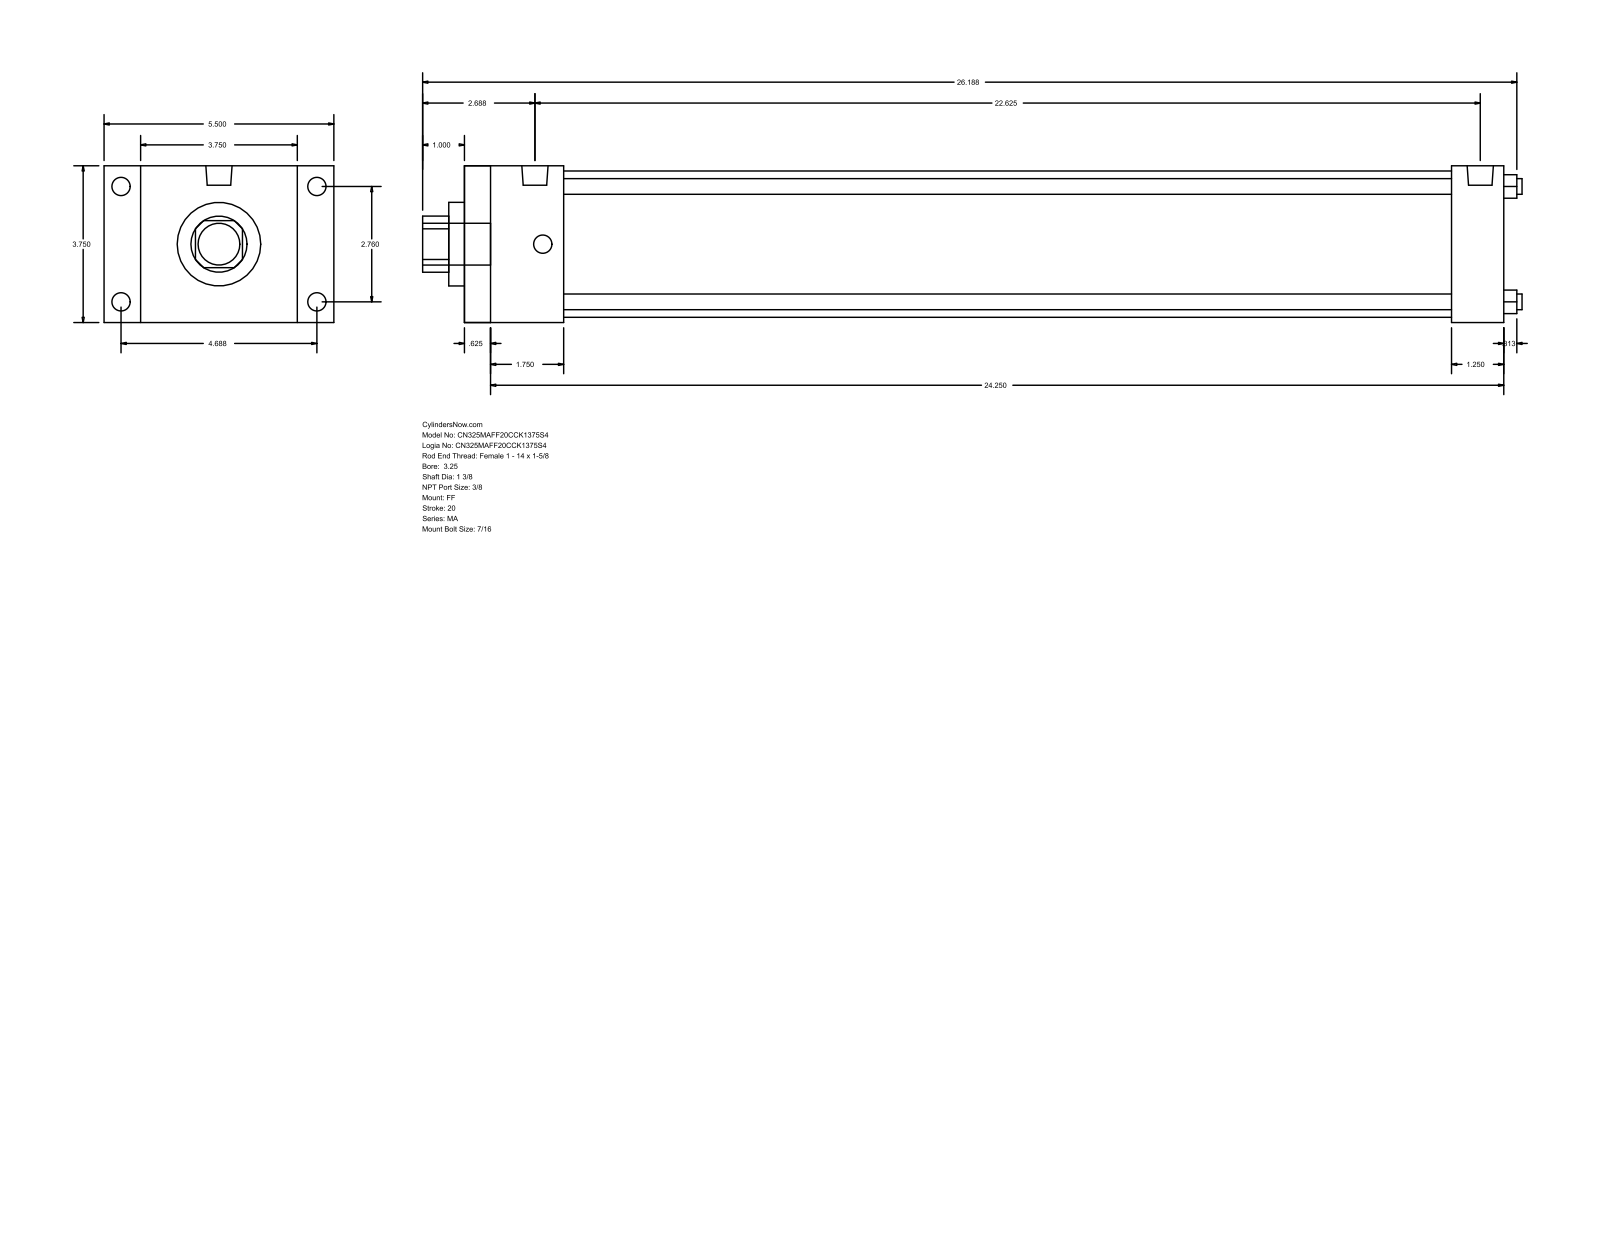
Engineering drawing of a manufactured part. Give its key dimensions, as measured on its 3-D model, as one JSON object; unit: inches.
{"part_name": "MA_FF__0325_1.375", "step_written_by": "GSSL Pune (CONFIG_CONTROL_DESIGN)", "units": "inches", "bodies": {"solids": 0, "faces": 92, "planar": 64, "cylindrical": 28, "other": 0}, "overall_size": [26.313, 5.5, 3.75], "round_holes": [[0.375, 4], [1.375, 1], [2, 1], [3.5, 1]], "round_bosses_or_shafts": [[0.437, 8], [0.627, 2], [1, 1]], "partial_cylinders_radius": [[0.672, 1]], "face_to_face_distances": [3.75, 24.875, 0.625, 24.25, 0.875, 4.625, 2.375, 23.625, 1.75, 23], "hole_center_spacings": [1.952, 2.76, 3.903]}
